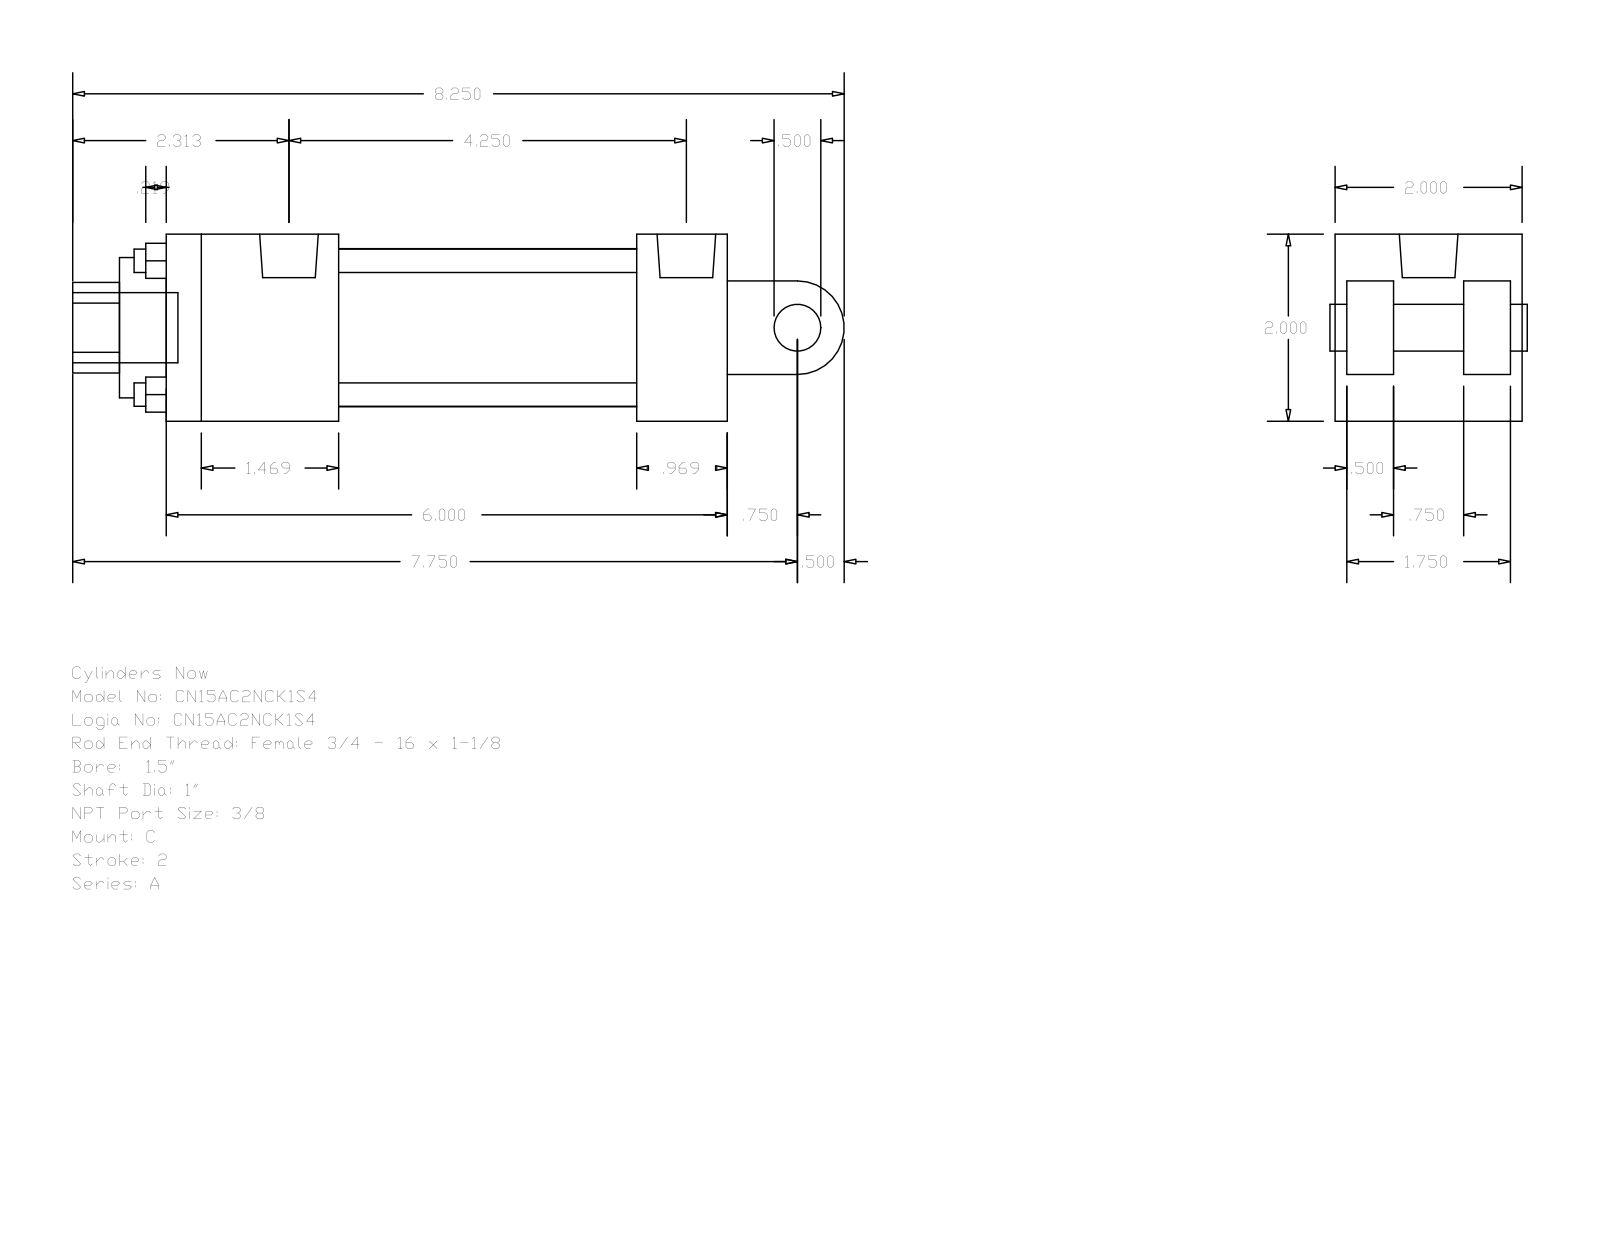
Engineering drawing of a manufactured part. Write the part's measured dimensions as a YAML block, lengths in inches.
part_name: "A_C__0150_1"
step_written_by: "GSSL Pune (CONFIG_CONTROL_DESIGN)"
units: inches
bodies: {solids: 0, faces: 99, planar: 70, cylindrical: 29, other: 0}
overall_size: [8.25, 2, 2]
round_holes:
  - {diameter: 0.25, count: 4}
  - {diameter: 0.219, count: 2}
  - {diameter: 0.627, count: 1}
  - {diameter: 1, count: 1}
  - {diameter: 1.5, count: 1}
  - {diameter: 1.69, count: 1}
round_bosses_or_shafts:
  - {diameter: 0.219, count: 2}
  - {diameter: 0.75, count: 1}
  - {diameter: 0.627, count: 1}
  - {diameter: 0.5, count: 1}
partial_cylinders:
  - {radius: 0.484, count: 1}
  - {radius: 0.5, count: 1}
face_to_face_distances: [2, 0.5, 0.125, 0.625, 1.875, 1.375, 1.25, 6, 5.031, 0.969]
hole_center_spacings: [1.011, 1.43, 2.022, 0.156]
